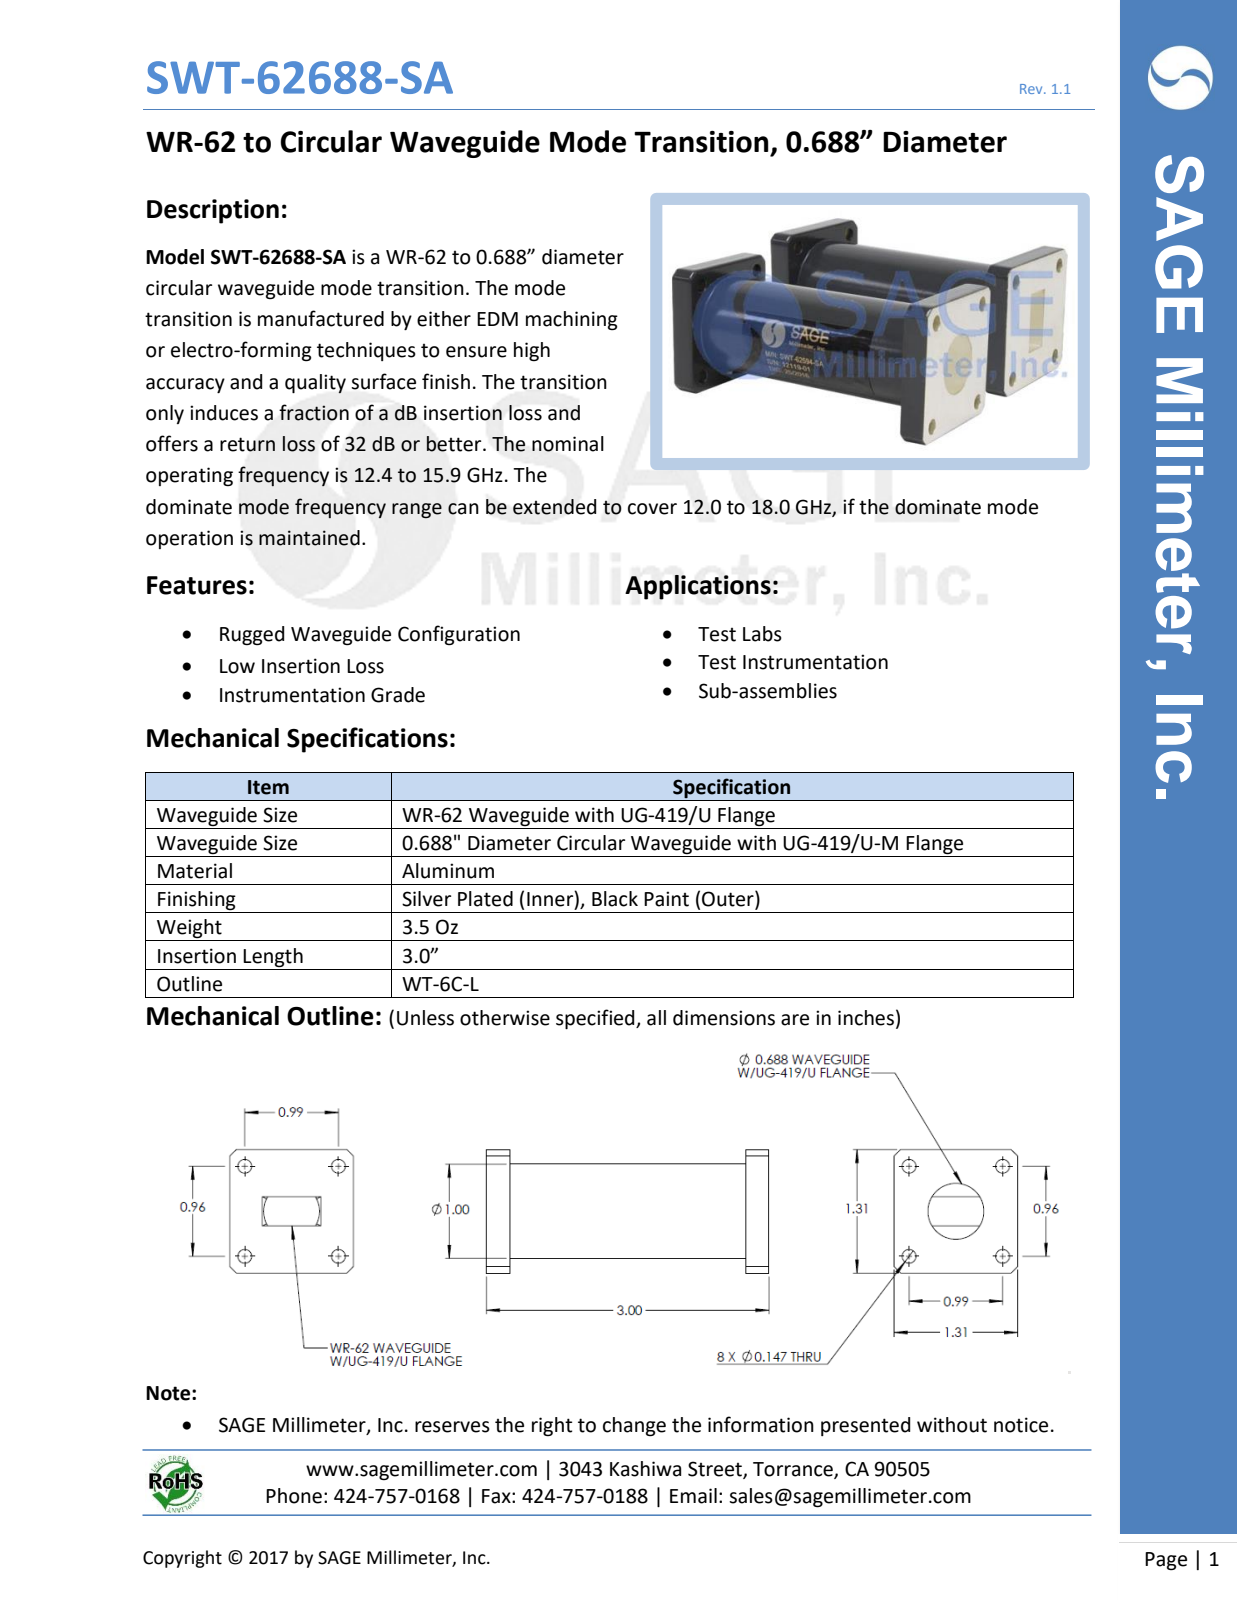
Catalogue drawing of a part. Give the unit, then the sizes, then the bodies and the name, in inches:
Units: inches
Overall size (bounding box): 3 × 1.312 × 1.312
Round holes (diameter × count): ⌀0.147 ×4, ⌀0.688 ×1
Round bosses / shafts (diameter × count): ⌀1 ×1
Main face-to-face distances: 0.25, 2.75, 3, 1.312, 2.5, 2.999, 0.249, 2.749, 2.998, 1.756
Hole centre spacings: 0.689, 0.69, 0.956, 0.994, 1.379
Volume: 2.785 in³ · Surface area: 16.33 in²
Bodies: 1 solid, 46 faces (26 planar, 20 cylindrical, 0 other)
Part name (STEP PRODUCT): SWT-62688-SA
STEP written by: SolidWorks 2016 (AUTOMOTIVE_DESIGN)
